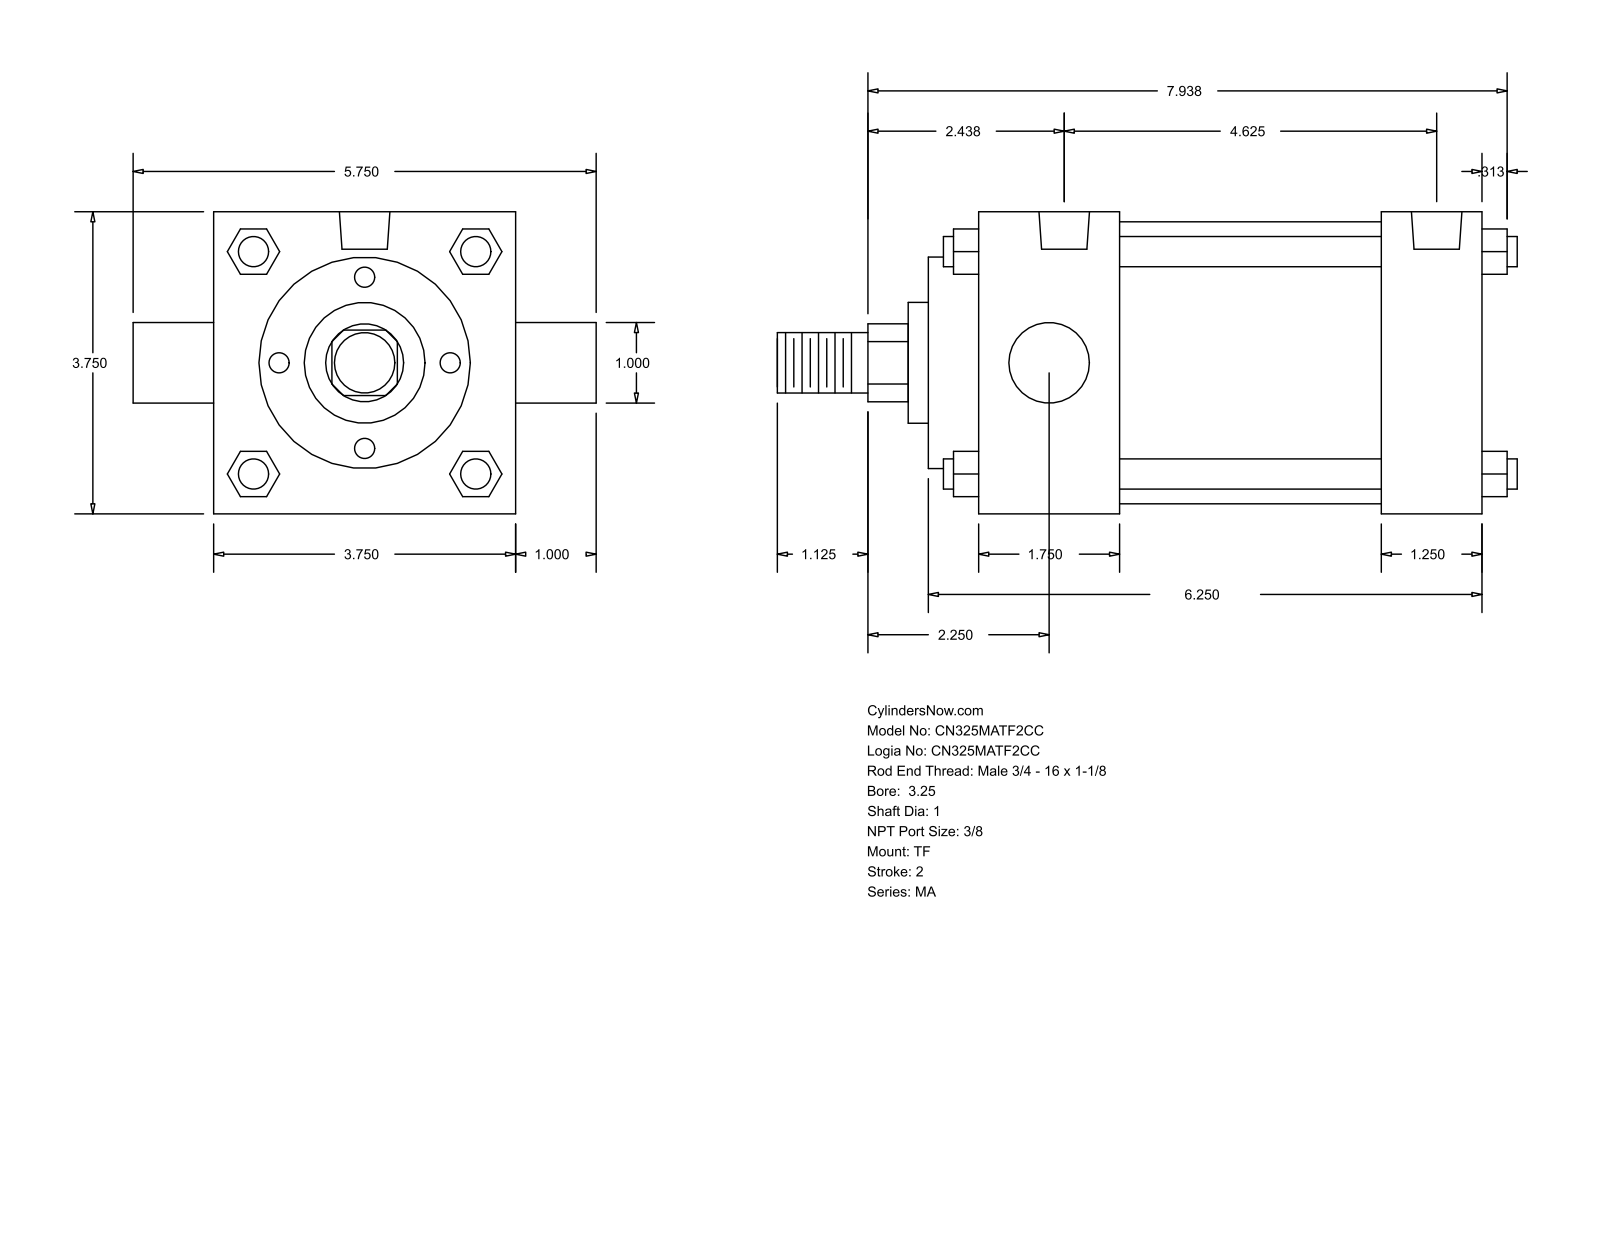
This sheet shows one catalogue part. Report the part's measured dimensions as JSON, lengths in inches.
{"part_name": "MA_TF__0325_1", "step_written_by": "GSSL Pune (CONFIG_CONTROL_DESIGN)", "units": "inches", "bodies": {"solids": 0, "faces": 122, "planar": 93, "cylindrical": 29, "other": 0}, "overall_size": [9.187, 5.75, 3.75], "round_holes": [[0.437, 3], [0.627, 2]], "round_bosses_or_shafts": [[0.375, 4], [1, 2], [3.5, 1], [2.625, 1], [1.5, 1], [0.75, 1]], "partial_cylinders_radius": [[0.484, 1]], "face_to_face_distances": [3.75, 6.25, 1.75, 5, 3.25, 4.5, 1.25, 0.625, 2.375, 5.625], "hole_center_spacings": [0.187, 0.188, 4.25, 4.437, 4.438, 4.625]}
